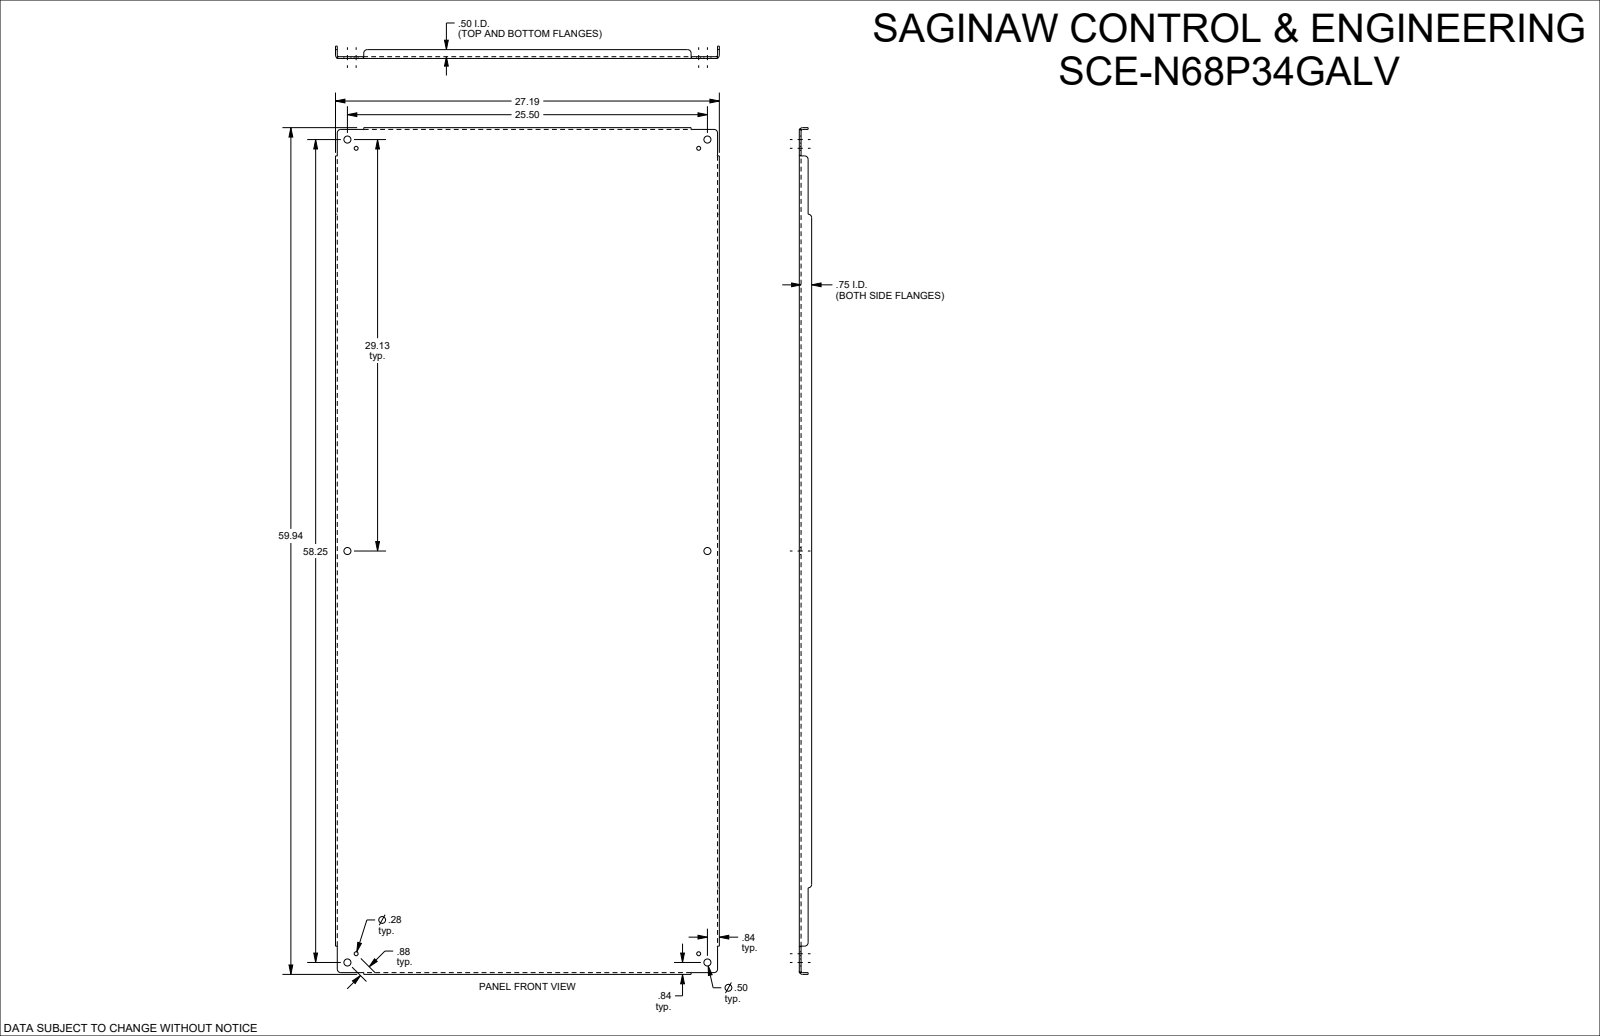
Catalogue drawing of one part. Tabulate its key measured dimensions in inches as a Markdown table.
| quantity | value |
| --- | --- |
| part name | SCE-N68P34GALV |
| STEP written by | SolidWorks 2023 (AUTOMOTIVE_DESIGN) |
| units | inches |
| bodies | 1 solid, 110 faces (42 planar, 44 cylindrical, 24 other) |
| overall size | 59.938 × 27.188 × 0.875 |
| volume | 214.6 in³ |
| surface area | 3 458 in² |
| round holes (diameter × count) | 0.5 × 6, 0.281 × 4 |
| partial cylindrical surfaces (radius × count) | 0.25 × 10, 0.112 × 4, 0.237 × 4 |
| main face-to-face distances | 0.125, 27.063, 26.938, 27.187, 0.125, 59.813, 0.75, 0.875, 59.687, 59.938 |
| hole center spacings | 0.875, 24.889, 28.513, 29.125, 37.837, 38.711, 57.634, 62.773 |
